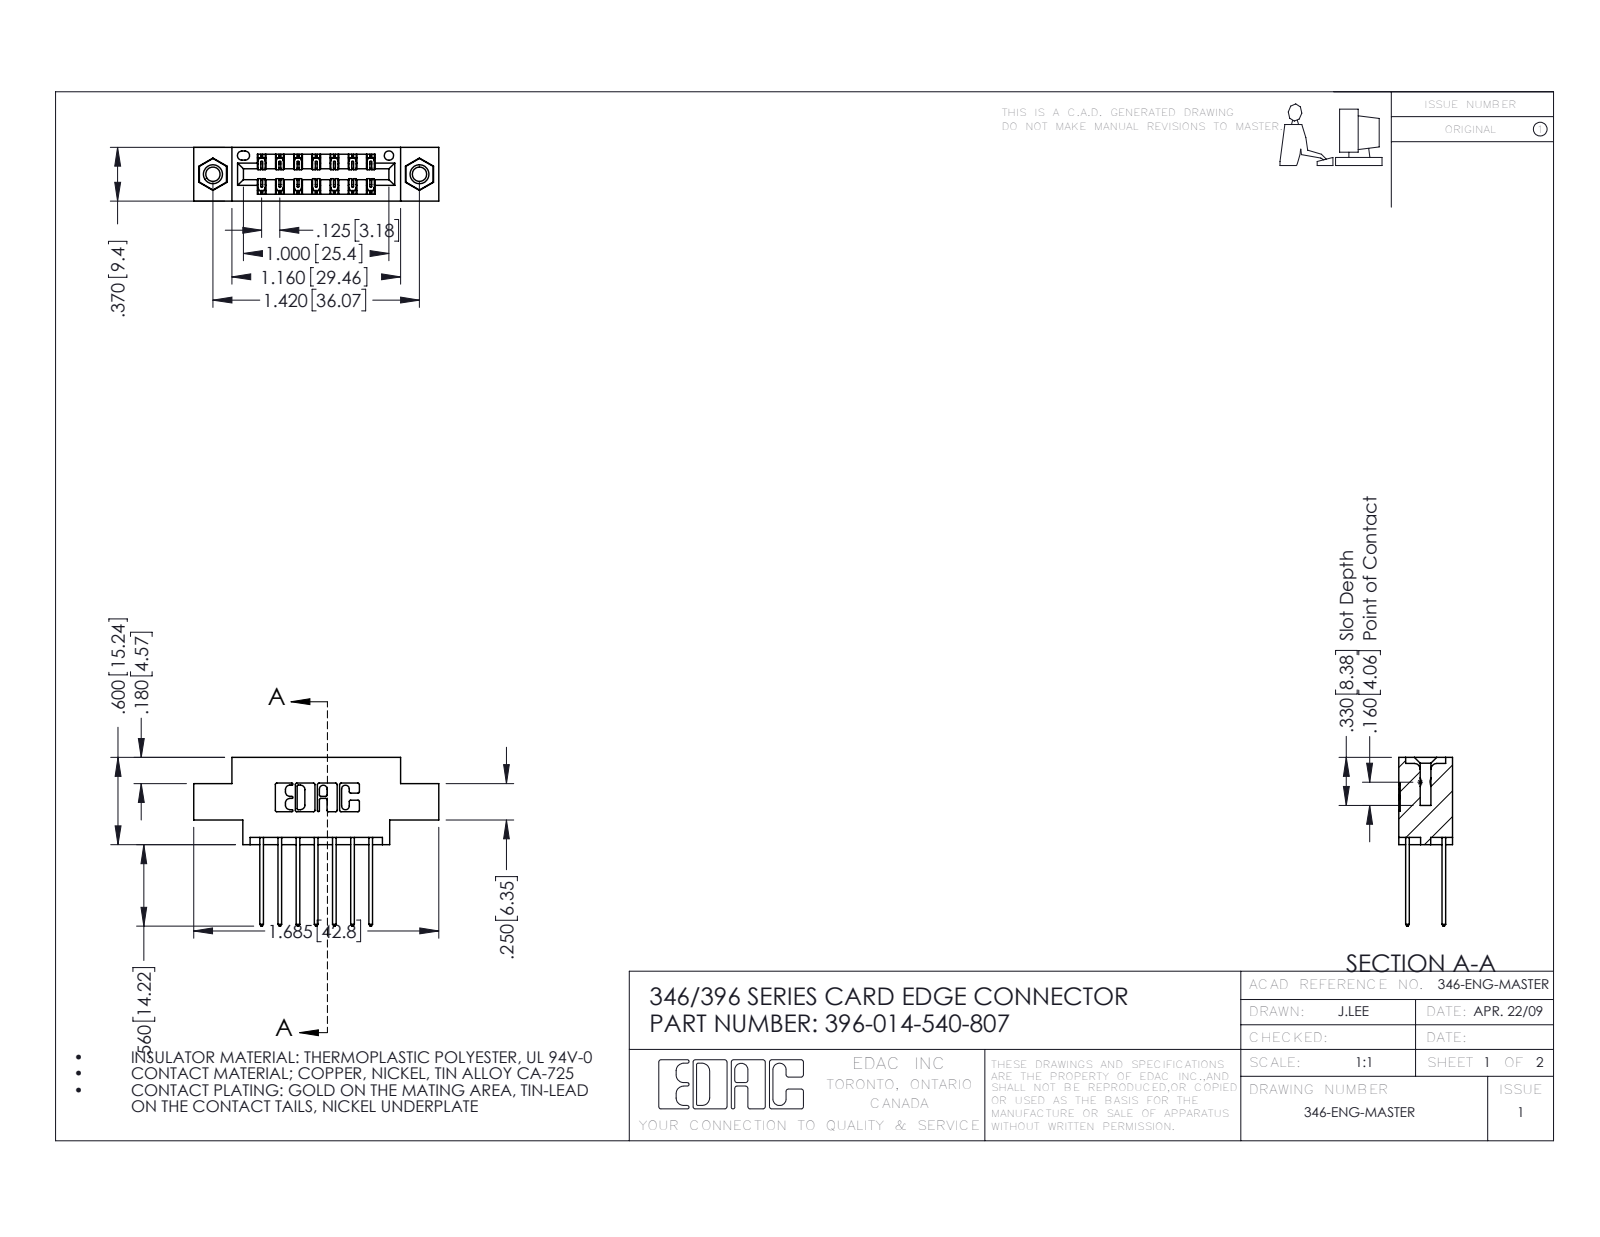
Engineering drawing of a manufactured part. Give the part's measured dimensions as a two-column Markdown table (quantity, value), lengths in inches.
| quantity | value |
| --- | --- |
| part name | 396-014-540-807; 345-292-001_345-293-140; 345-250-001_345-250-005-103; 346 Part_0.170 Offset - 0.156 Dia-TI |
| STEP written by | SolidWorks 2016 (CONFIG_CONTROL_DESIGN) |
| units | inches |
| bodies | 17 solids, 914 faces (602 planar, 296 cylindrical, 16 other) |
| overall size | 1.685 × 1.16 × 0.37 |
| volume | 0.231 in³ |
| surface area | 7.935 in² |
| round holes (diameter × count) | 0.098 × 2, 0.125 × 2, 0.156 × 2, 0.064 × 1 |
| round bosses / shafts (diameter × count) | 0.155 × 2 |
| partial cylindrical surfaces (radius × count) | 0.01 × 22, 0.006 × 21, 0.01 × 14, 0.007 × 6, 0.031 × 6, 0.026 × 3, 0.014 × 2, 0.022 × 2 |
| main face-to-face distances | 0.25, 0.048, 0.322, 0.37, 0.072, 0.298, 0.025, 0.275, 0.222, 0.148 |
| hole center spacings | 0.246, 1.217, 1.42 |
